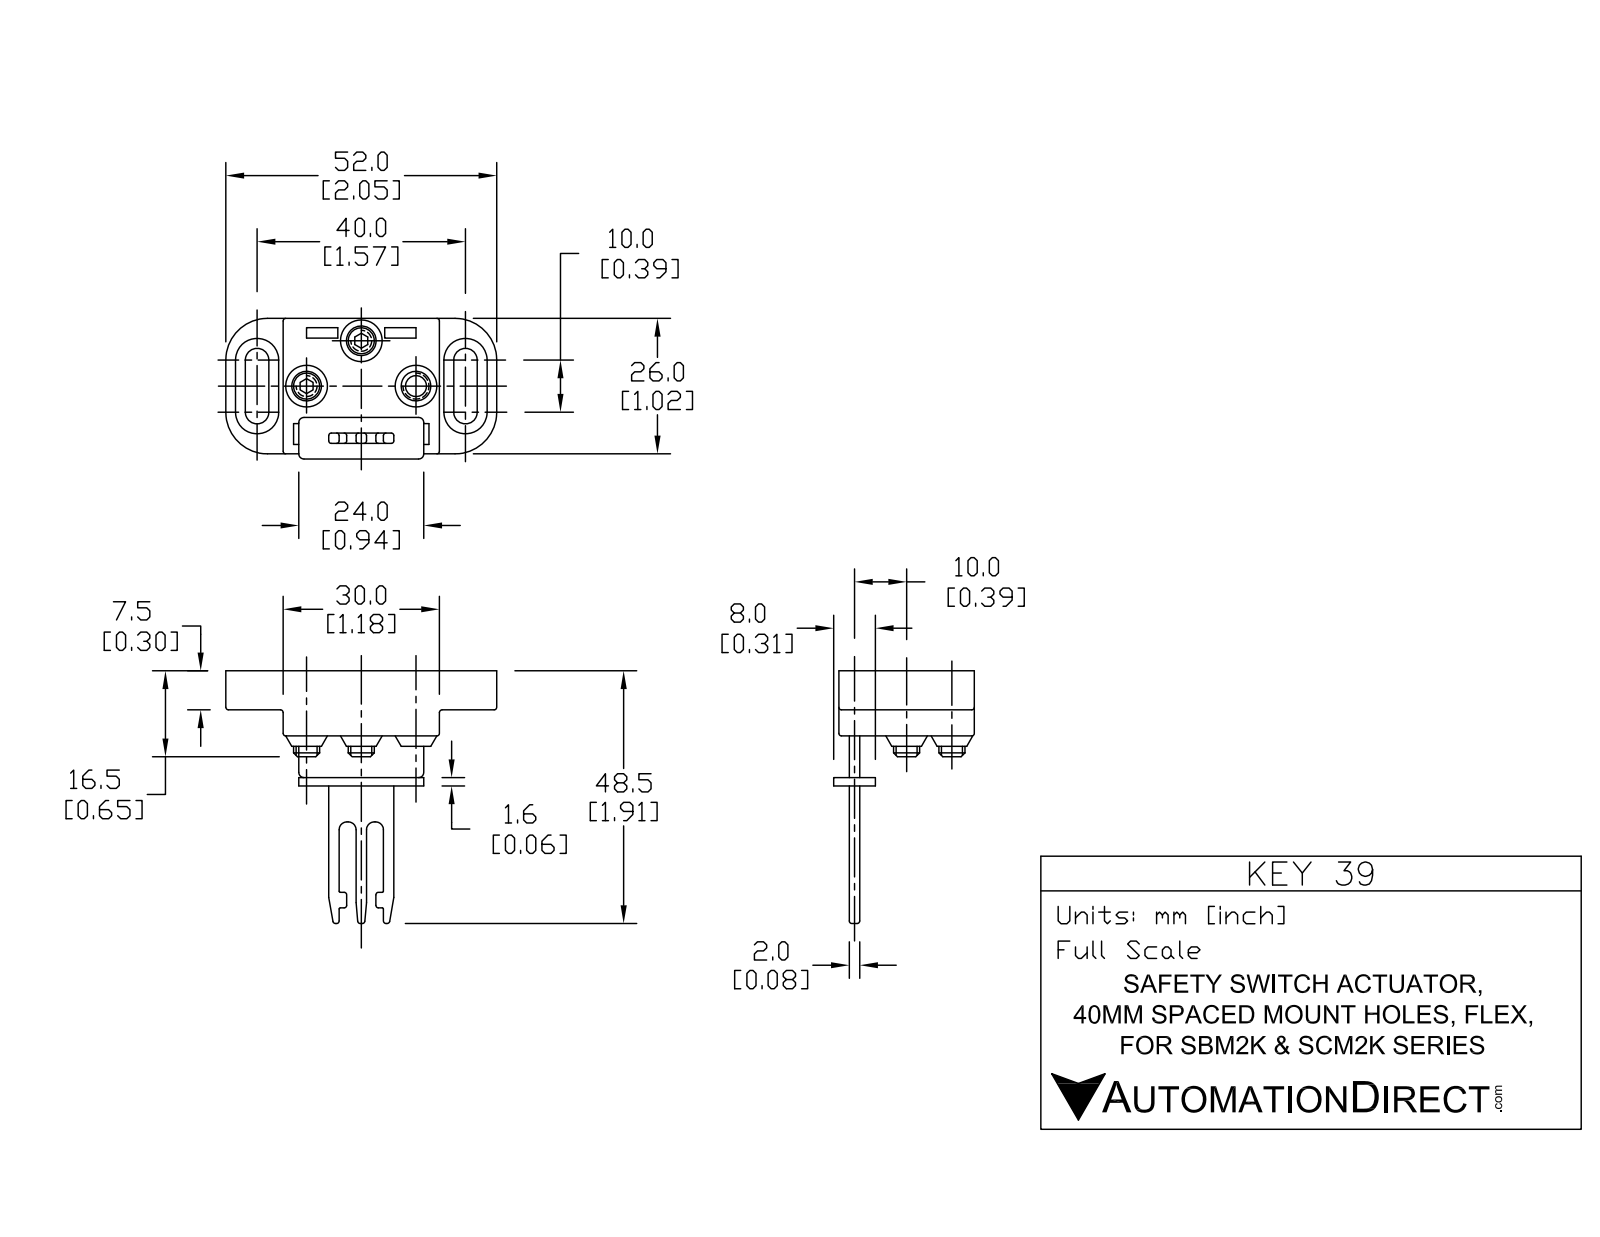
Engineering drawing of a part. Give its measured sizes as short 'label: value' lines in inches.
name: KEY39
written by: SolidWorks 2018 (AUTOMOTIVE_DESIGN)
unit: in
bodies: 4 solids, 275 faces (104 planar, 113 cylindrical, 58 other)
size: 2.047 × 1.909 × 1.055
volume: 0.482 in³; area: 13.49 in²
holes: 3× ⌀0.157, 3× ⌀0.197
rounds: 54× R0.02, 8× R0.039, 6× R0.087, 4× R0.008, 4× R0.059, 4× R0.089, 4× R0.163, 4× R0.315
face distances: 0.079, 0.071, 0.953, 1.024, 0.157, 0.413, 0.492, 0.197, 0.087, 0.118
hole spacings: 0.537, 0.827
